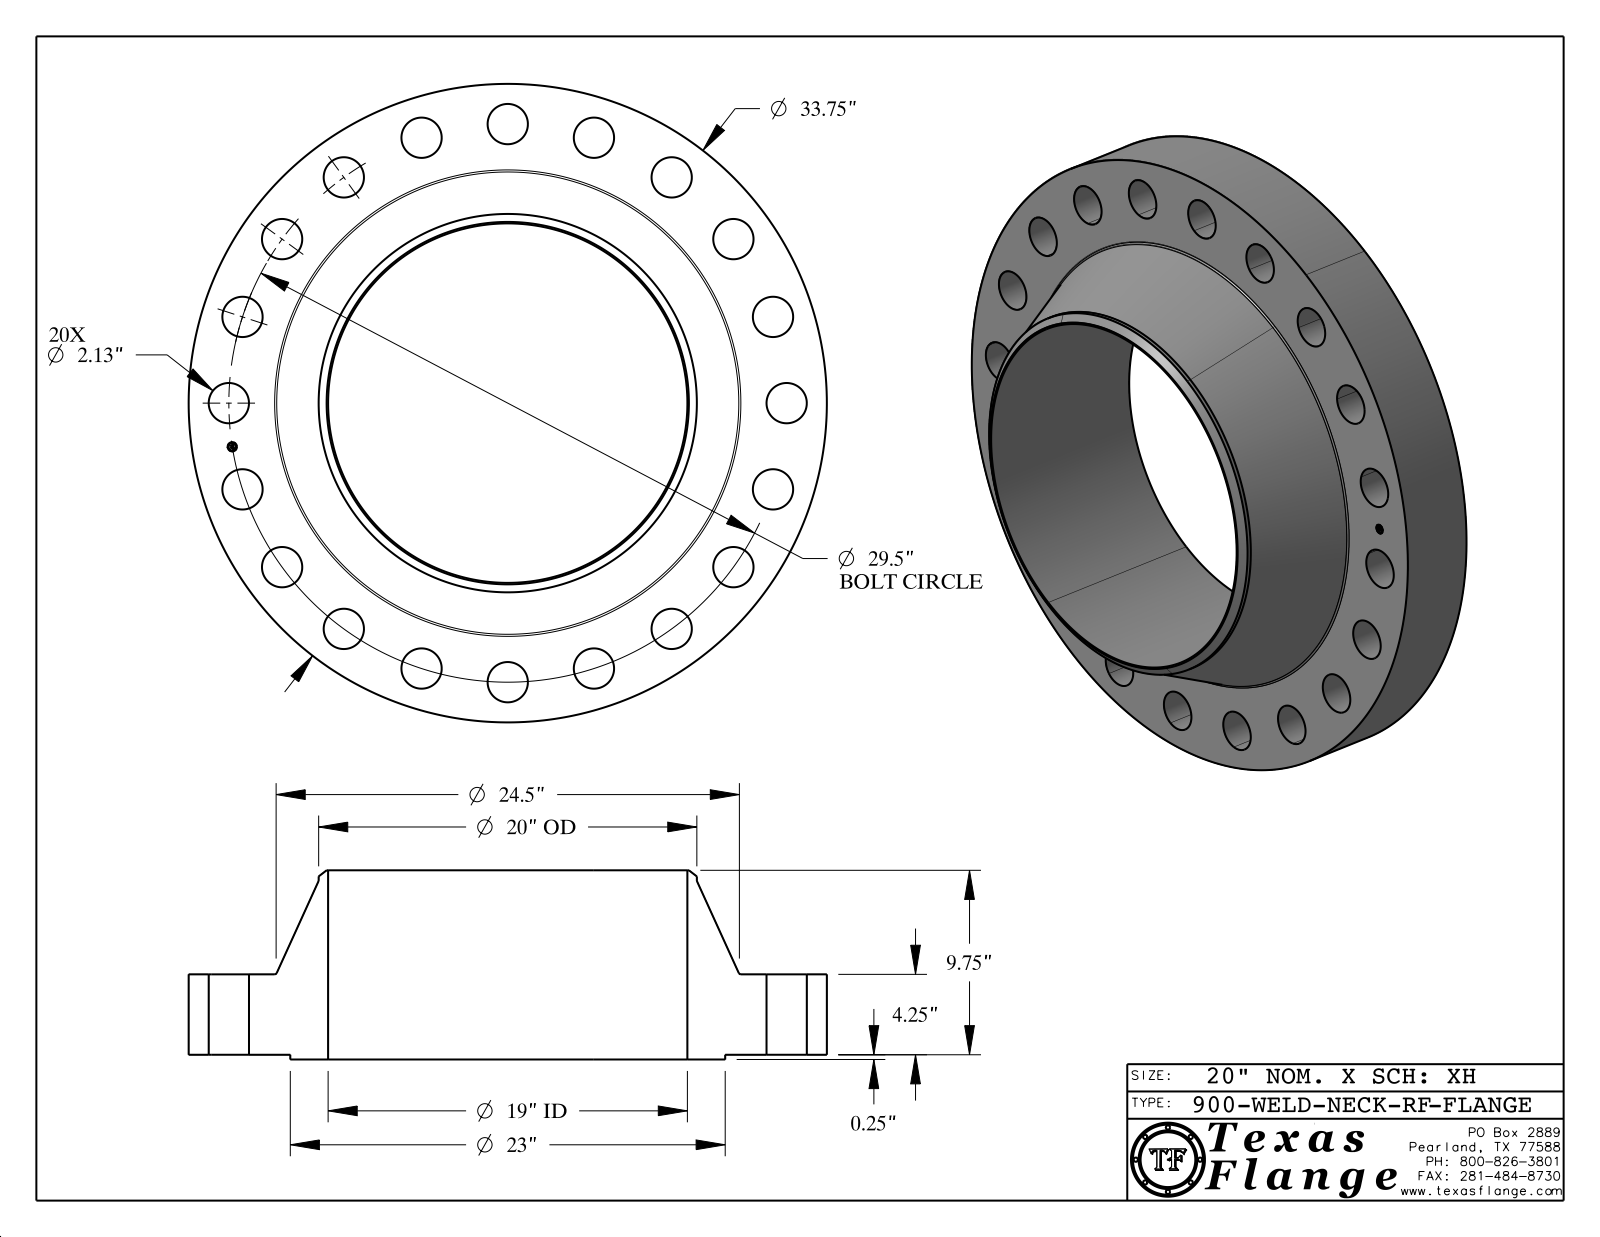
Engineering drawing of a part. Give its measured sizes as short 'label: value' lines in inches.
name: 900-WELD-NECK-RF
written by: CATIA V5 STEP AP214 (AUTOMOTIVE_DESIGN)
unit: in
bodies: 1 solid, 443 faces (369 planar, 68 cylindrical, 6 other)
size: 33.75 × 33.75 × 10
volume: 2 867 in³; area: 2 957 in²
holes: 20× ⌀2.13, 1× ⌀0.495, 1× ⌀19
bosses: 8× ⌀0.03, 1× ⌀33.75, 1× ⌀23, 1× ⌀20, 1× ⌀0.39
face distances: 4.25, 0.25, 4.5, 10, 9.75, 5.5, 4.485, 4.235, 0.015, 5.515
hole spacings: 14.75, 29.137, 4.615, 17.34, 20.859, 23.866, 26.285, 9.116
